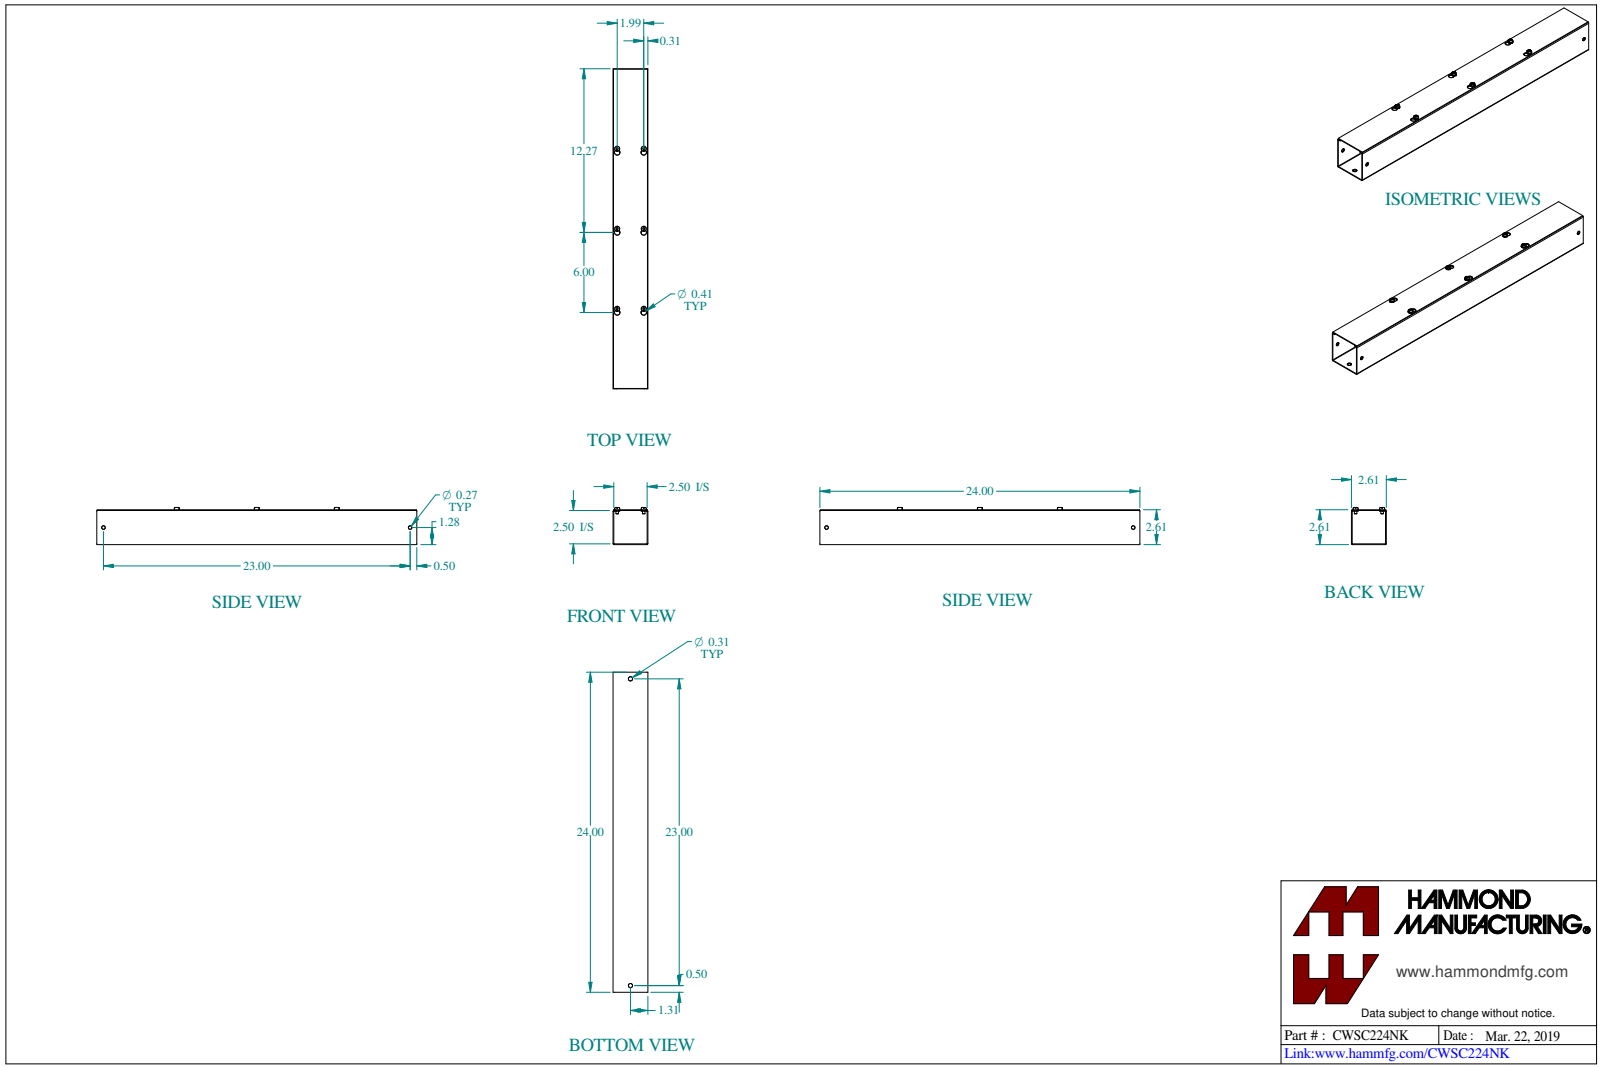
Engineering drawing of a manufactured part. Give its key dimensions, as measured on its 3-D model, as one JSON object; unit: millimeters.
{"part_name": "CWSC224NK", "step_written_by": "SolidWorks 2023 (CONFIG_CONTROL_DESIGN)", "units": "millimeters", "bodies": {"solids": 8, "faces": 234, "planar": 118, "cylindrical": 80, "other": 36}, "overall_size": [609.6, 70.8, 66.4], "volume_mm3": 245300, "surface_area_mm2": 342900, "round_holes": [[4.5, 6], [6.8, 2], [8, 2]], "round_bosses_or_shafts": [[9.5, 6], [4.8, 6]], "partial_cylinders_radius": [[3.2, 6], [5.2, 6], [0.7, 4], [2.2, 4]], "face_to_face_distances": [1.4, 64.9, 63.5, 66.4, 62.1, 2.9, 0.8, 65.6, 0.7, 64.2], "hole_center_spacings": [142, 152.4, 160.6, 293.2, 445.2, 50.5, 304.8, 309]}
